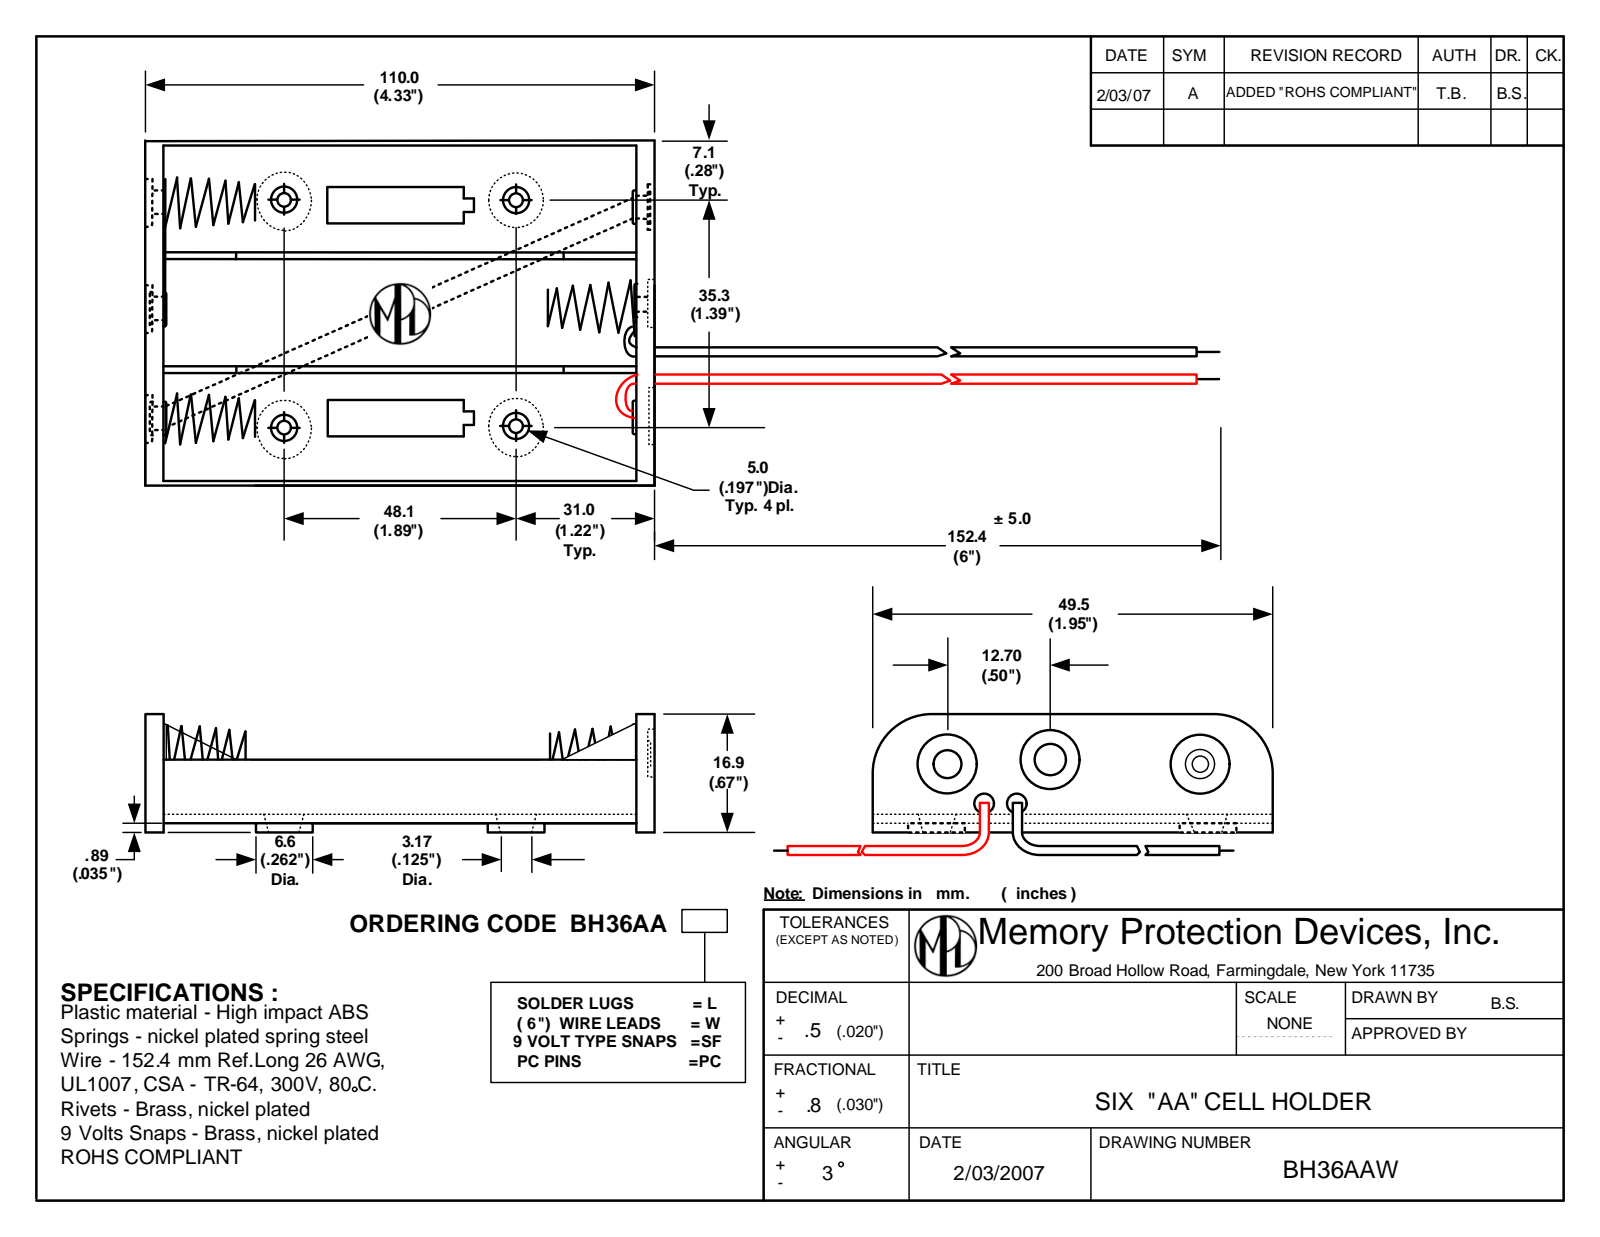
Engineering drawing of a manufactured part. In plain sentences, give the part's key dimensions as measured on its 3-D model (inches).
The part is named "BH36AAW". Its 3-D file was written by "SolidWorks 2017 (AUTOMOTIVE_DESIGN)". It is 13 solids with 419 faces: 211 planar, 148 cylindrical and 60 other. Overall it measures 10.236 by 1.949 by 0.665 inches. Its volume is 1.048 cubic inches and its surface area 41.26 square inches. Round holes: 6 of diameter 0.138, 4 of diameter 0.125, 4 of diameter 0.197, 3 of diameter 0.055, 3 of diameter 0.087, 3 of diameter 0.295, 2 of diameter 0.023. Round bosses or shafts: 6 of diameter 0.169, 4 of diameter 0.26, 3 of diameter 0.138, 3 of diameter 0.134, 2 of diameter 0.055, 1 of diameter 0.028. Partial cylindrical surfaces (rounded edges, fillets, slot ends): 2 of radius 0.177, 1 of radius 0.024. The main face-to-face distances are 0.063, 0.675, 1.274, 0.624, 1.325, 0.051, 0.65, 1.262, 1.886, 0.561. The hole center spacings are 0.65, 3.062, 1.299, 2.992, 0.393, 0.478, 0.549, 0.553.
